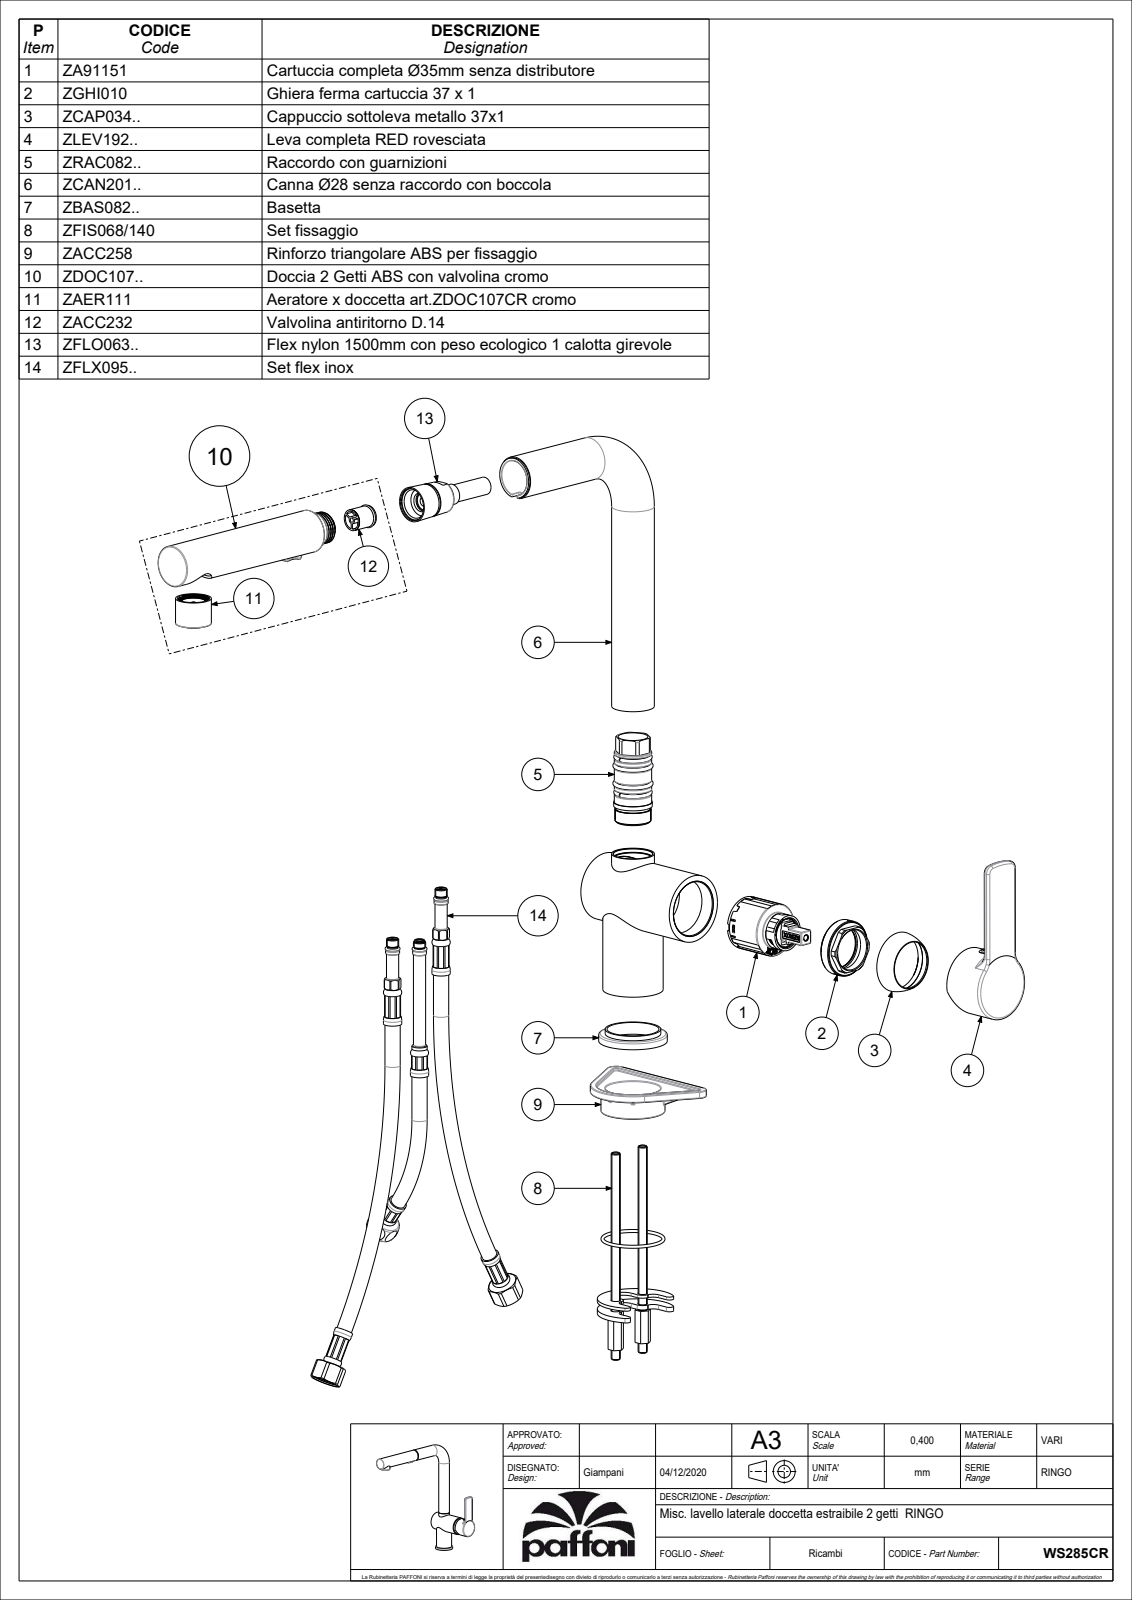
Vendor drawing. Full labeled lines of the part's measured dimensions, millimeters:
Part name (STEP PRODUCT): WS285CR
STEP written by: CREO PARAMETRIC BY PTC INC, 2020044 (CONFIG_CONTROL_DESIGN)
Units: millimetres
Bodies: 2 solids, 2407 faces (1194 planar, 640 cylindrical, 573 other)
Overall size (bounding box): 287.4 × 260.5 × 118.63
Volume: 202 520 mm³ · Surface area: 154 908 mm²
Round holes (diameter × count): ⌀6.5 ×3, ⌀7 ×3, ⌀8.6 ×3, ⌀9.4 ×3, ⌀5.5 ×2, ⌀25 ×2, ⌀36 ×2, ⌀3 ×1, ⌀3.4 ×1, ⌀3.5 ×1, ⌀4 ×1, ⌀4.5 ×1
Round bosses / shafts (diameter × count): ⌀21 ×3, ⌀28 ×2, ⌀20 ×2, ⌀45 ×1, ⌀44.7 ×1, ⌀43 ×1, ⌀39.6 ×1, ⌀38.5 ×1
Partial cylindrical surfaces — rounded edges, fillets, slot ends (radius × count): R0.5 ×93, R0.2 ×42, R0.3 ×25, R24.3 ×12, R1 ×10, R1.5 ×9, R1.7 ×6, R5 ×6
Main face-to-face distances: 4.54, 2, 70.8, 4.5, 15, 11.2, 21, 1.5, 76.75, 5.95
Hole centre spacings: 10.79, 11.18, 12.21, 12.98, 19.91, 24.83, 4.75, 10.01
